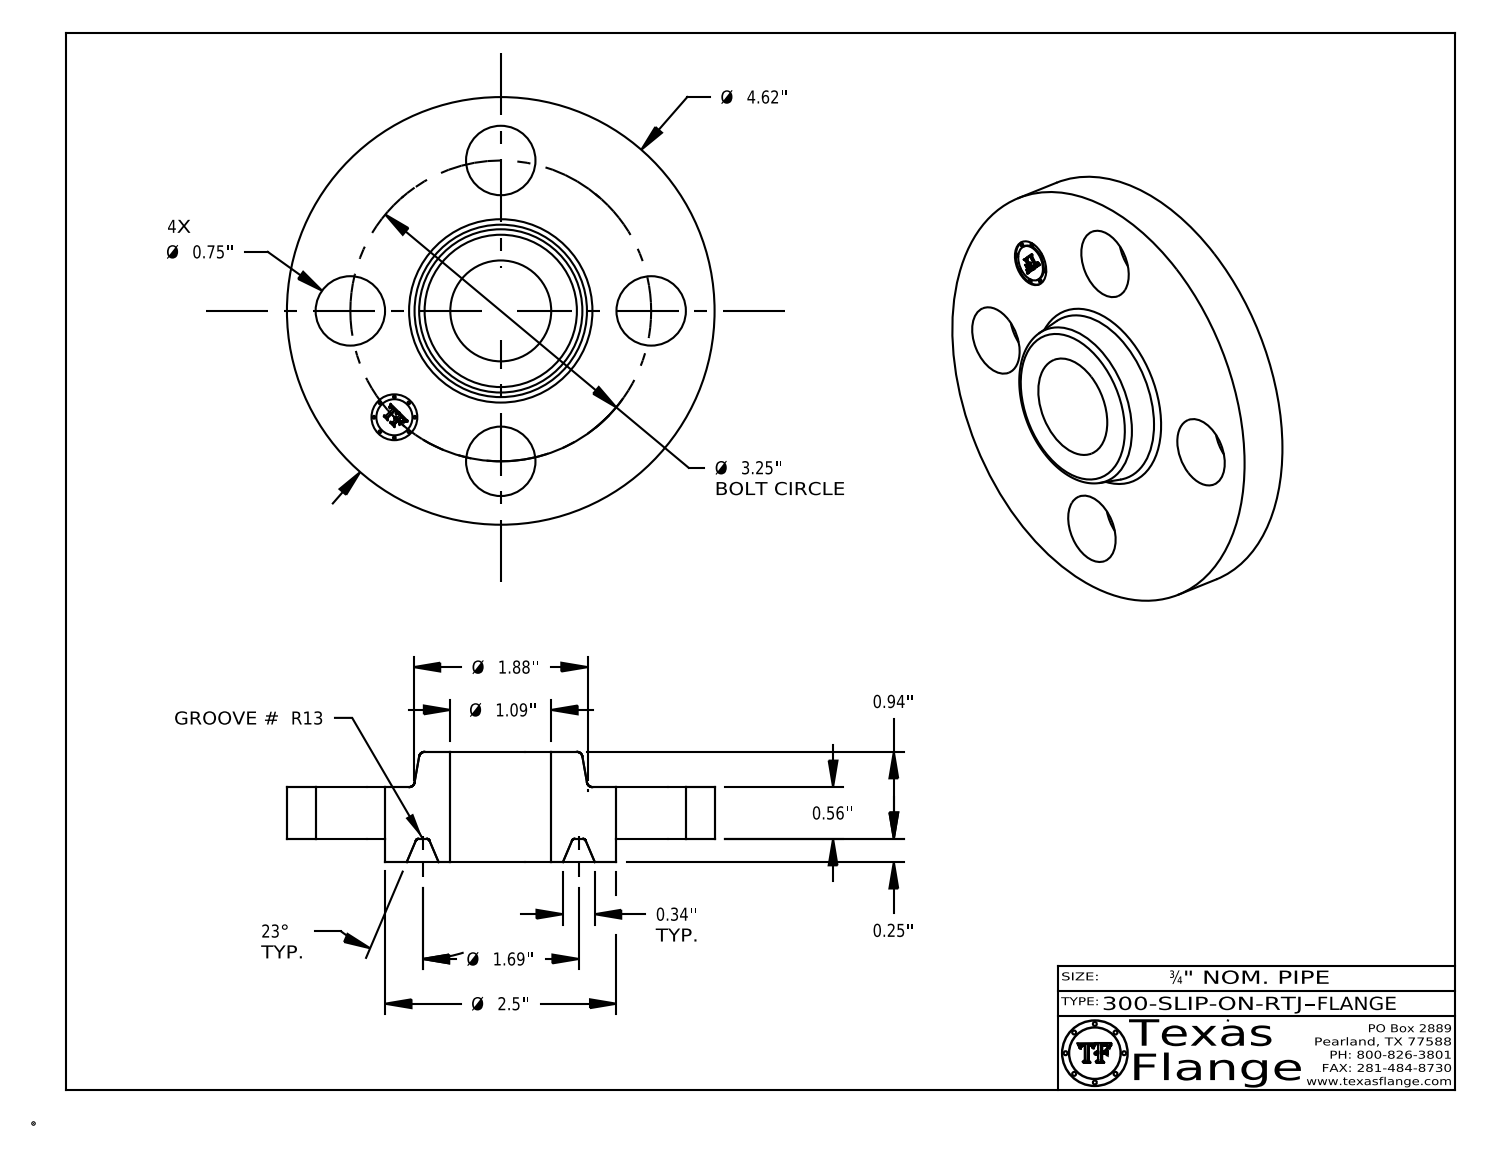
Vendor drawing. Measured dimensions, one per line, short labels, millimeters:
name: 300-SLIP-ON-RTJ
written by: CATIA V5 STEP AP214 (AUTOMOTIVE_DESIGN)
unit: mm
bodies: 1 solid, 419 faces (371 planar, 34 cylindrical, 14 other)
size: 117.3 × 117.3 × 30.2
volume: 150 400 mm³; area: 32 900 mm²
holes: 4× ⌀19.1, 1× ⌀12.6, 1× ⌀27.7
bosses: 8× ⌀0.8, 1× ⌀117.3, 1× ⌀63.5, 1× ⌀9.9
face distances: 14.2, 6.4, 20.6, 30.2, 23.9, 9.7, 20.2, 13.8, 0.4, 10
hole spacings: 41.3, 58.4, 31.6, 76.3, 82.6
